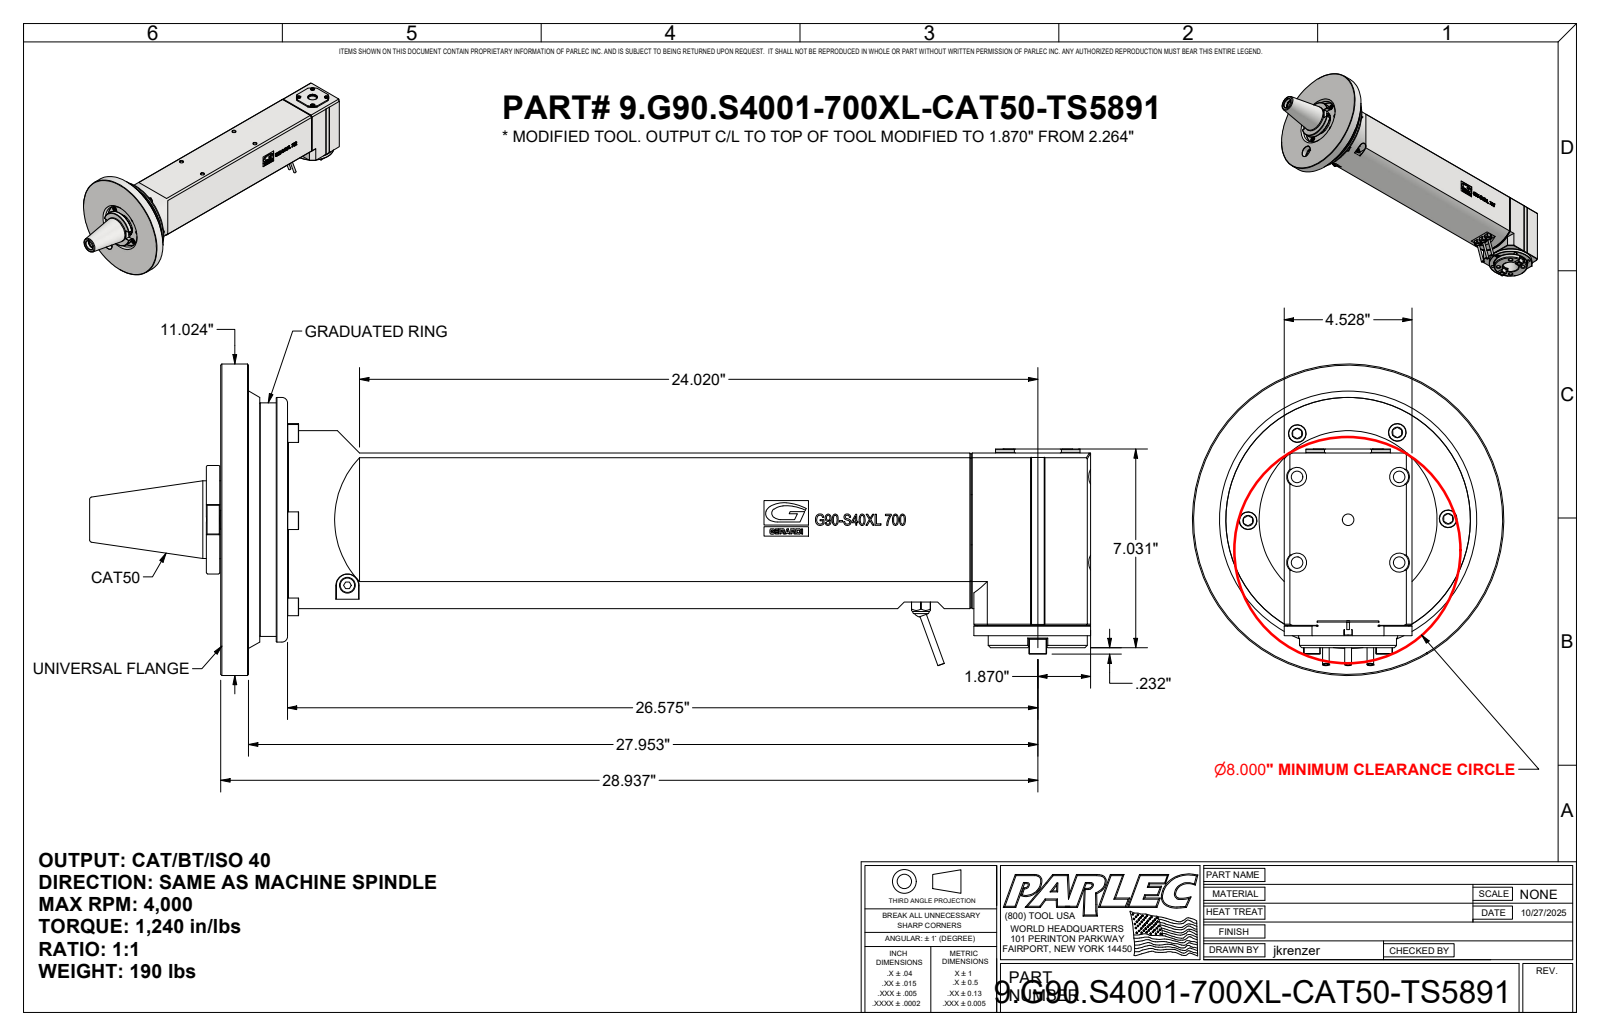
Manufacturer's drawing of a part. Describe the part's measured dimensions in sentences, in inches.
The part is named "9.G90.S4001-700XL-CAT50-TS5891; 9.G90.S4001-700XL-TS5891 (GEARBOX ONLY); 9_SK_45_1 (Classic, Cat50, MTC); 9_UF_00005 (Clas". Its 3-D file was written by "Autodesk Inventor 2025 (AUTOMOTIVE_DESIGN)". It is 18 solids with 2173 faces: 829 planar, 487 cylindrical and 857 other. Overall it measures 35.449 by 11.024 by 11.024 inches. Its volume is 709.8 cubic inches and its surface area 2 103 square inches. Round holes: 18 of diameter 0.335, 12 of diameter 0.268, 12 of diameter 0.551, 11 of diameter 0.354, 11 of diameter 0.413, 10 of diameter 0.197, 10 of diameter 0.394, 8 of diameter 0.346, 6 of diameter 0.157, 6 of diameter 0.236, 5 of diameter 0.217, 5 of diameter 0.669. Round bosses or shafts: 6 of diameter 0.63, 4 of diameter 0.512, 4 of diameter 0.386, 4 of diameter 0.315, 3 of diameter 0.236, 2 of diameter 2.165, 2 of diameter 1.378, 2 of diameter 0.551. Partial cylindrical surfaces (rounded edges, fillets, slot ends): 48 of radius 0.02, 36 of radius 0.118, 7 of radius 0.394, 6 of radius 0.512, 6 of radius 0.531, 3 of radius 0.386, 2 of radius 0.157, 2 of radius 0.197. The main face-to-face distances are 4.528, 1.378, 0.394, 0.984, 0.591, 0.787, 1.772, 30.807, 30.217, 29.823. The hole center spacings are 2.362, 3.125, 3.543, 1.969, 3.105, 3.989, 5.148, 1.181.
